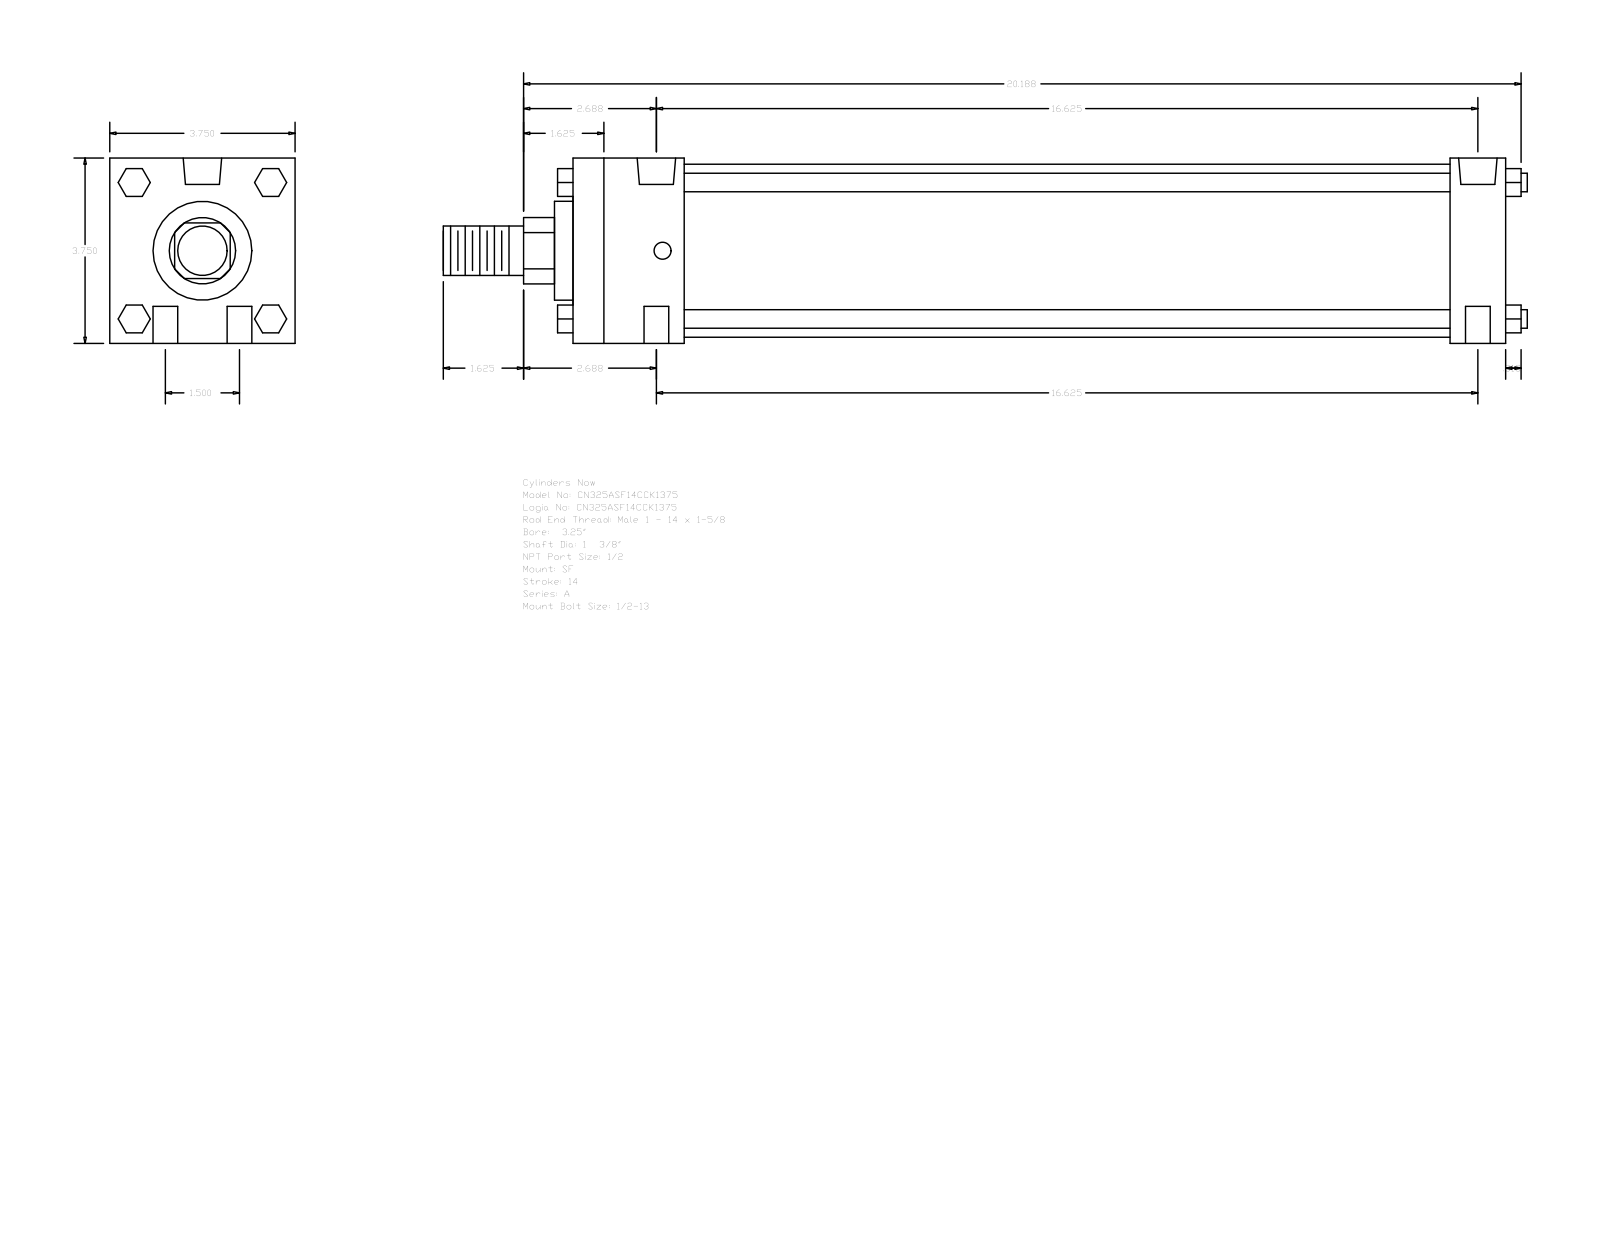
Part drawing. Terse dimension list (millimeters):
name: A_SF__0325_1.375
written by: GSSL Pune (CONFIG_CONTROL_DESIGN)
unit: mm
bodies: 0 solids, 124 faces (94 planar, 30 cylindrical, 0 other)
size: 557.21 × 95.25 × 95.25
holes: 4× ⌀12.7, 2× ⌀8.73, 2× ⌀19.77
bosses: 4× ⌀9.53, 1× ⌀88.9, 1× ⌀50.8, 1× ⌀34.92, 1× ⌀25.4
rounds: 1× R17.06
face distances: 95.24, 479.42, 57.15, 450.85, 28.57, 393.7, 422.27, 66.67, 9.52, 460.37
hole spacings: 19.05, 422.71, 422.28, 38.1, 424, 415.92
